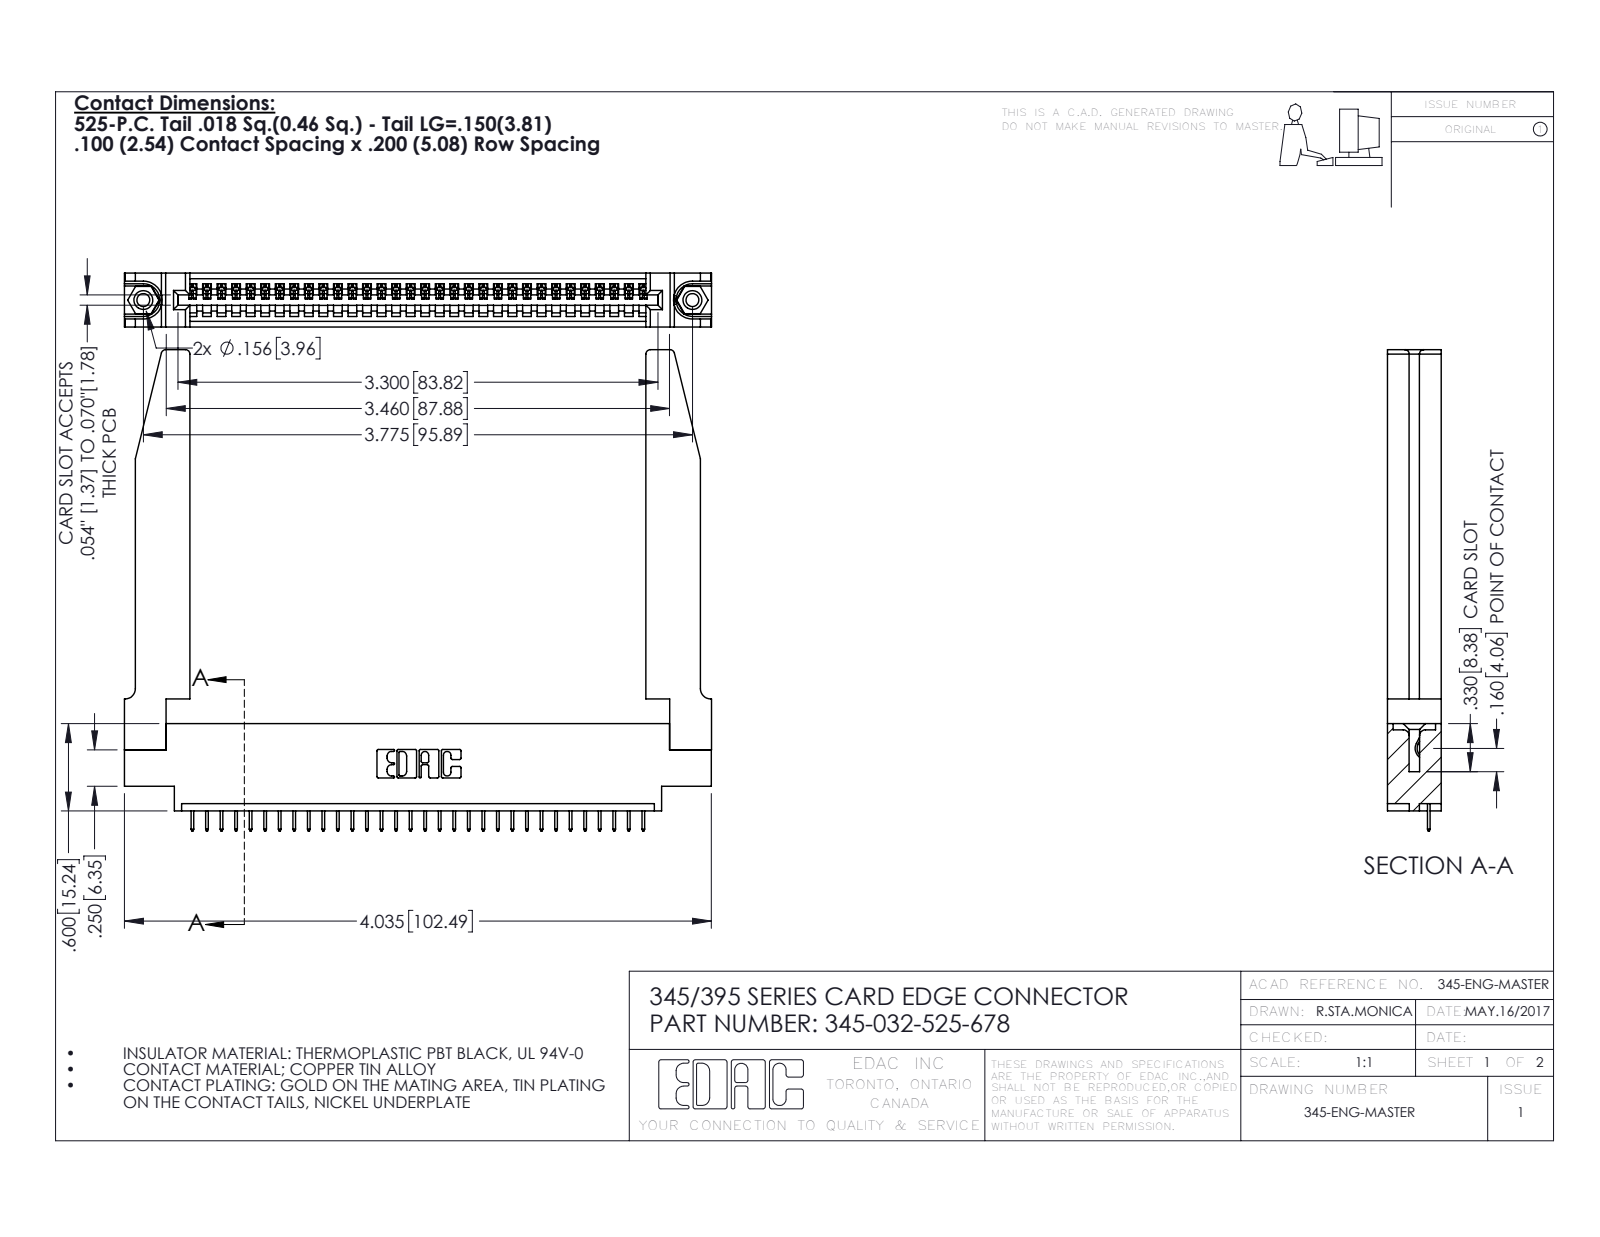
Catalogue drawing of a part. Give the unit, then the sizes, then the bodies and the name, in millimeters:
Units: millimetres
Overall size (bounding box): 102.5 × 84 × 9.4
Round holes (diameter × count): ⌀2.3 ×2, ⌀3.2 ×2, ⌀4 ×2, ⌀1.6 ×1
Round bosses / shafts (diameter × count): ⌀3.9 ×2
Partial cylindrical surfaces — rounded edges, fillets, slot ends (radius × count): R0.2 ×64, R0.3 ×22, R0.8 ×8, R0.2 ×6, R0.8 ×6, R0.7 ×3, R0.8 ×2, R1 ×2
Main face-to-face distances: 9.4, 1.8, 7.6, 2.5, 6.9, 0.6, 5.1, 3.8, 3.8, 5.7
Hole centre spacings: 6.9, 89.9, 95.9
Volume: 17 170 mm³ · Surface area: 18 910 mm²
Bodies: 37 solids, 2348 faces (1698 planar, 598 cylindrical, 52 other)
Part name (STEP PRODUCT): 345-032-525-678; 345-220-078_345-220-078; 345 Part_0.170 Offset - 0.156 Dia-TH; 345-250-001_345-250-001-102 (+1 more)
STEP written by: SolidWorks 2020 (CONFIG_CONTROL_DESIGN)
